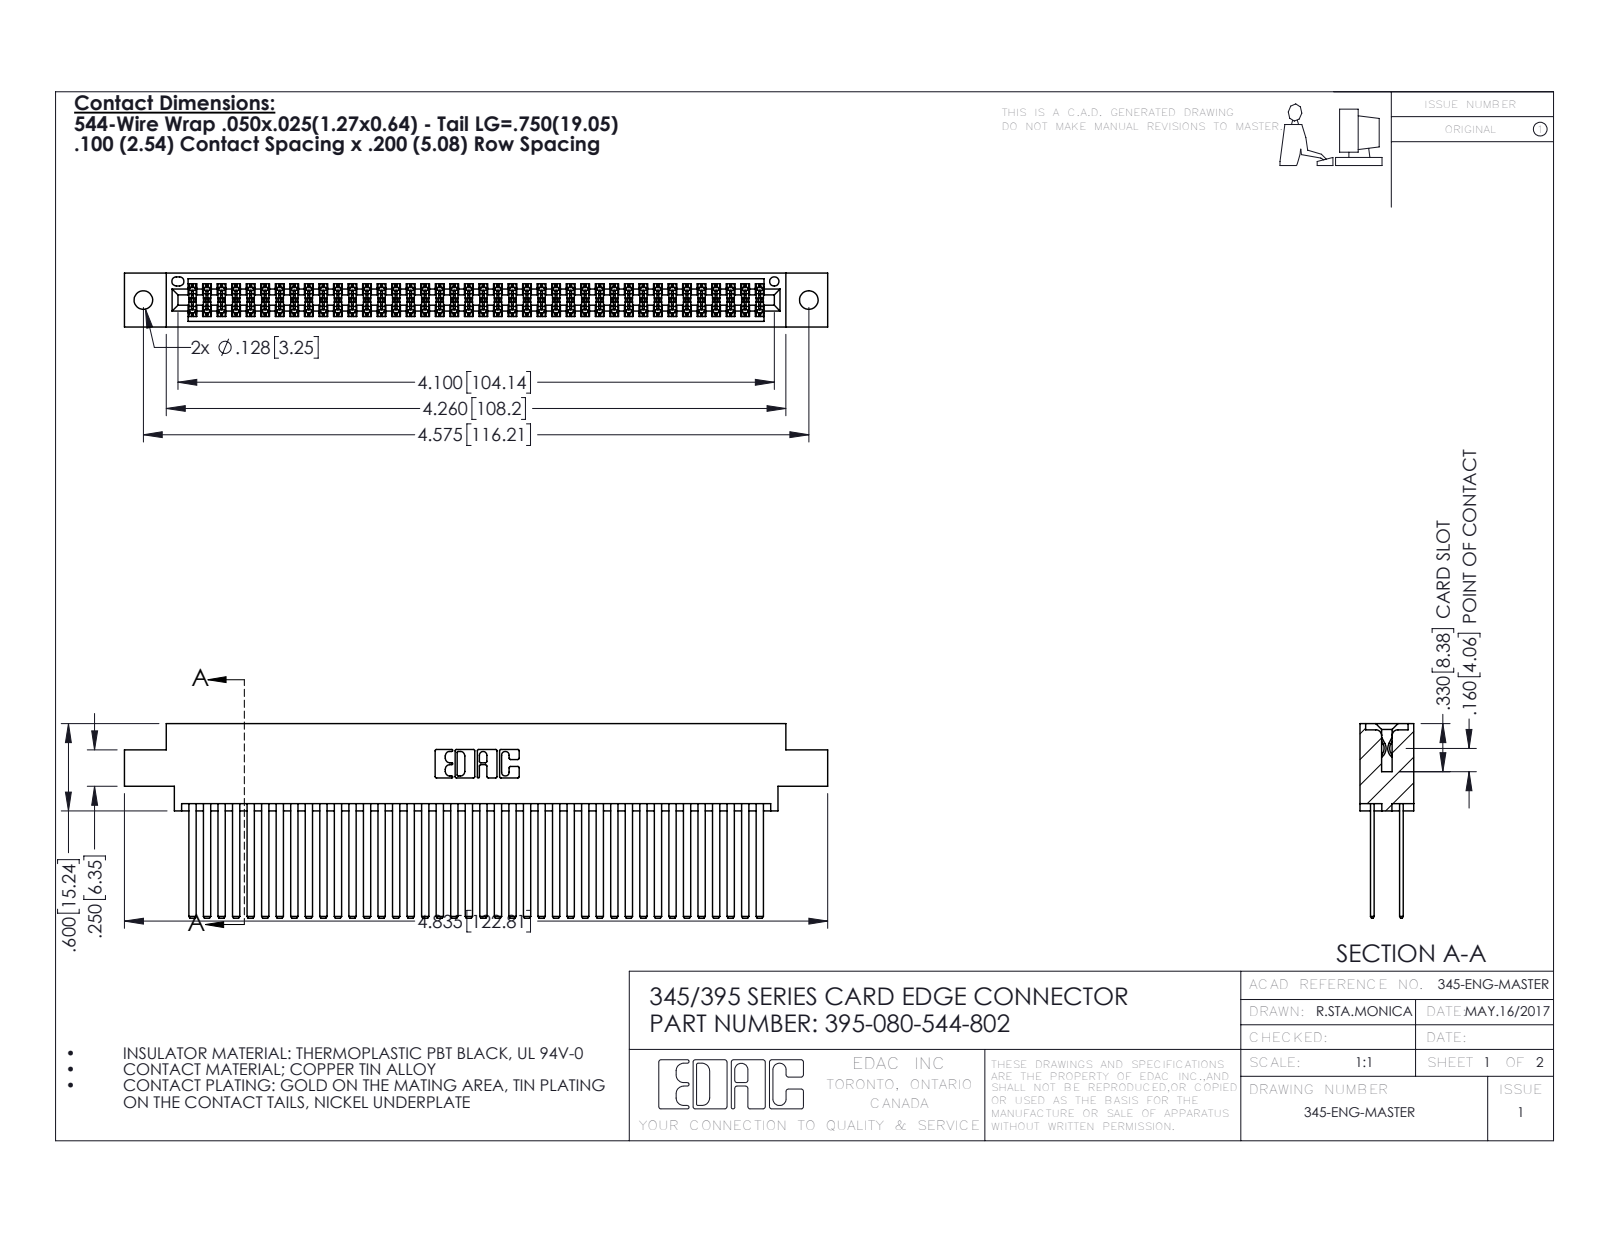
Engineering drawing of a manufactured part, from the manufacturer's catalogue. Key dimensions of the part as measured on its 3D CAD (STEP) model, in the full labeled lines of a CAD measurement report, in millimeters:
Part name (STEP PRODUCT): 395-080-544-802; 345-292-001_345-293-144; 345 Part_0.170 Offset - 0.128 Dia
STEP written by: SolidWorks 2016 (CONFIG_CONTROL_DESIGN)
Units: millimetres
Bodies: 81 solids, 3650 faces (2404 planar, 1246 cylindrical, 0 other)
Overall size (bounding box): 122.8 × 34 × 9.4
Volume: 12 900 mm³ · Surface area: 22 160 mm²
Round holes (diameter × count): ⌀3.3 ×2, ⌀1.6 ×1
Partial cylindrical surfaces — rounded edges, fillets, slot ends (radius × count): R0.2 ×120, R0.3 ×22, R0.2 ×6, R0.8 ×6, R0.7 ×3, R0.4 ×2, R0.5 ×2, R0.6 ×2
Main face-to-face distances: 5.1, 0.6, 1.8, 2.5, 6.9, 7.6, 5.7, 4.4, 9.4, 3.8
Hole centre spacings: 6.9, 110.2, 116.2
